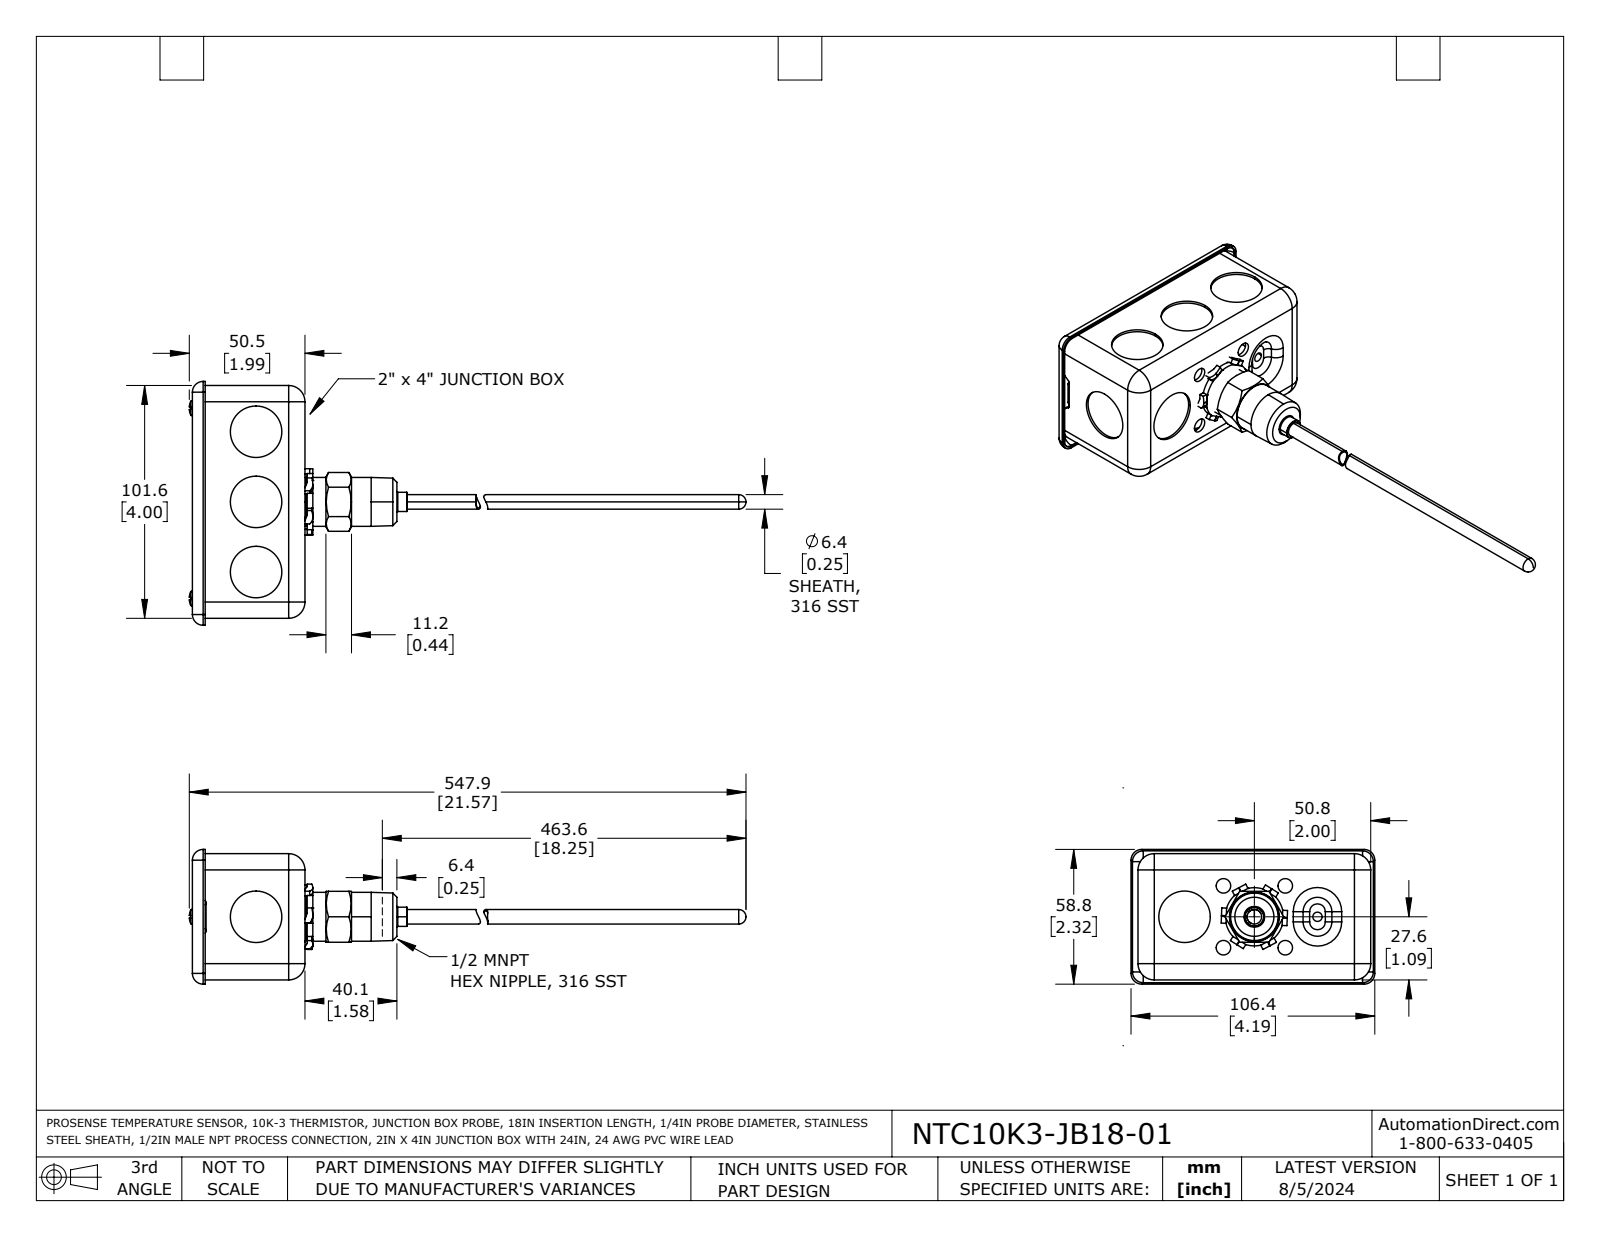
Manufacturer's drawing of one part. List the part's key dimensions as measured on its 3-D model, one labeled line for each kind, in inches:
Part name (STEP PRODUCT): NTC10K3-JB18-01
STEP written by: SolidWorks 2021 (AUTOMOTIVE_DESIGN)
Units: inches
Bodies: 5 solids, 365 faces (154 planar, 145 cylindrical, 66 other)
Overall size (bounding box): 21.563 × 4.19 × 2.315
Volume: 3.288 in³ · Surface area: 118.9 in²
Round holes (diameter × count): ⌀0.885 ×6, ⌀0.25 ×4, ⌀0.115 ×2, ⌀0.16 ×1, ⌀0.21 ×1, ⌀0.253 ×1, ⌀0.438 ×1
Round bosses / shafts (diameter × count): ⌀0.136 ×2, ⌀0.84 ×1, ⌀0.33 ×1, ⌀0.25 ×1
Partial cylindrical surfaces — rounded edges, fillets, slot ends (radius × count): R0.185 ×16, R0.245 ×8, R0.28 ×8, R0.174 ×6, R0.555 ×6, R0.045 ×4, R0.165 ×4, R0.07 ×2
Main face-to-face distances: 0.07, 0.03, 2.03, 2.1, 0.04, 0.1, 0.06, 1.855, 2.07, 2
Hole centre spacings: 0.751, 1.062, 1.248, 2.254, 0.767, 0.854, 1.205, 1.502
